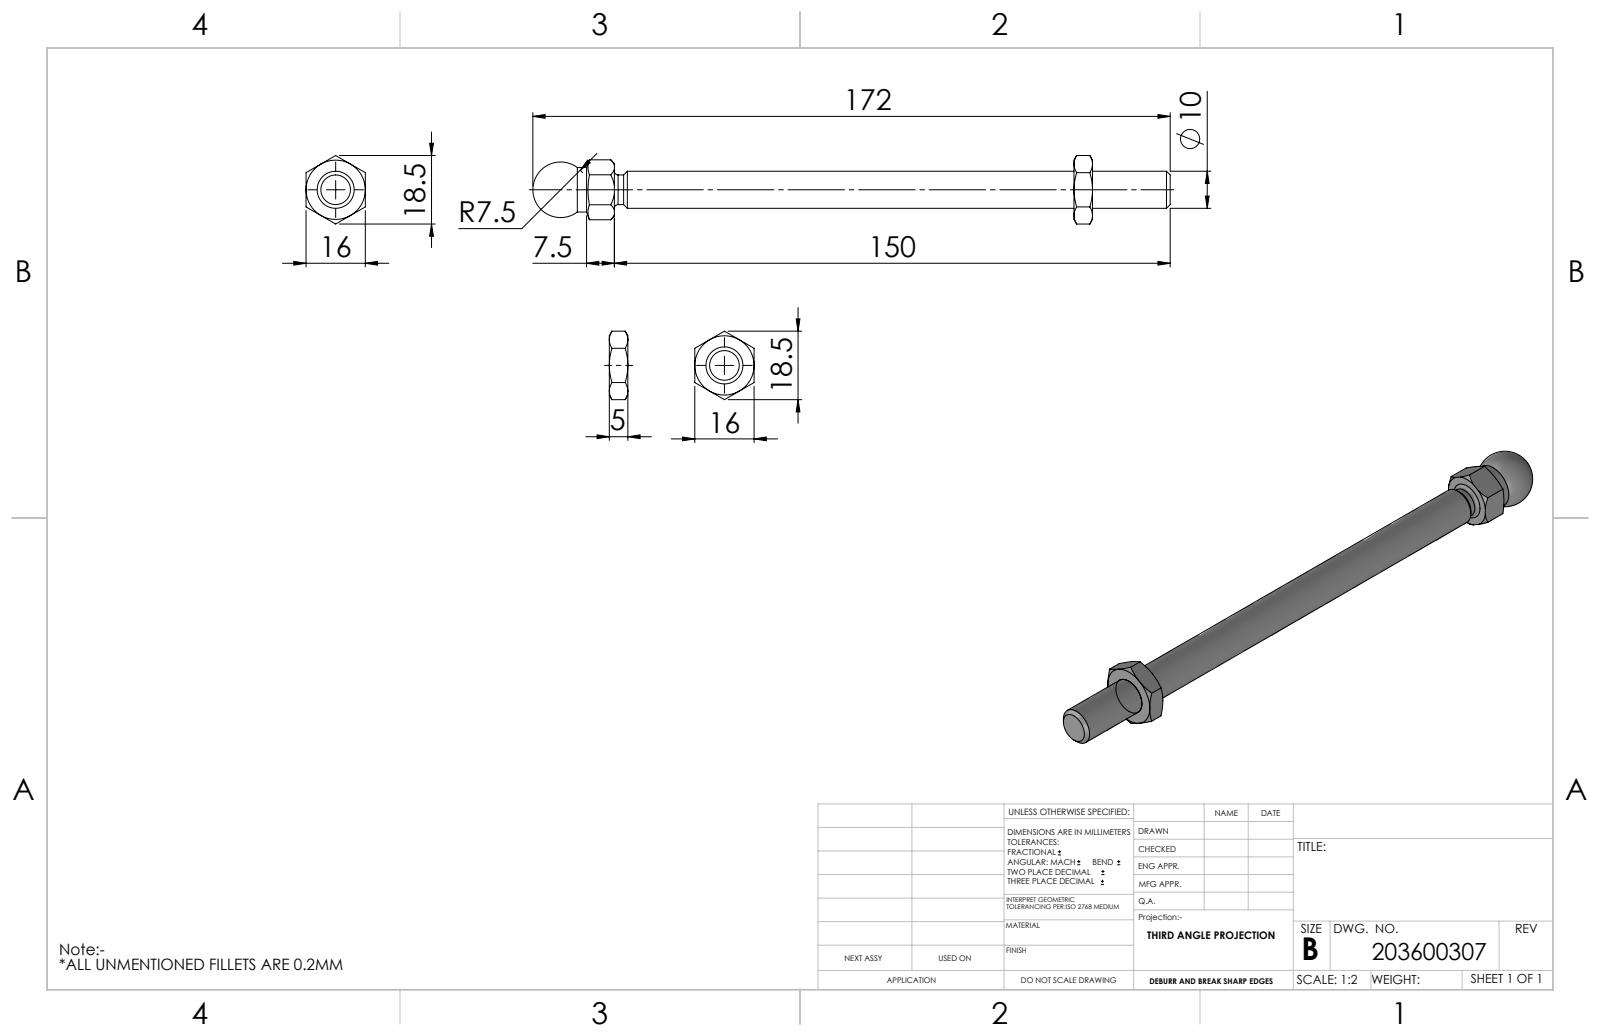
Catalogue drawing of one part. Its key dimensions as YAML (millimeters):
part_name: "203600307_c_1"
step_written_by: "SolidWorks 2014 (CONFIG_CONTROL_DESIGN)"
units: millimeters
bodies: {solids: 2, faces: 81, planar: 16, cylindrical: 16, other: 49}
overall_size: [172, 18.48, 16]
volume: 15578
surface_area: 6701
round_holes:
  - {diameter: 8.5, count: 1}
  - {diameter: 10, count: 1}
round_bosses_or_shafts:
  - {diameter: 12, count: 1}
  - {diameter: 8, count: 1}
face_to_face_distances: [1, 15, 14, 16, 5, 124.04, 129.04, 150, 25.96, 20.96]
